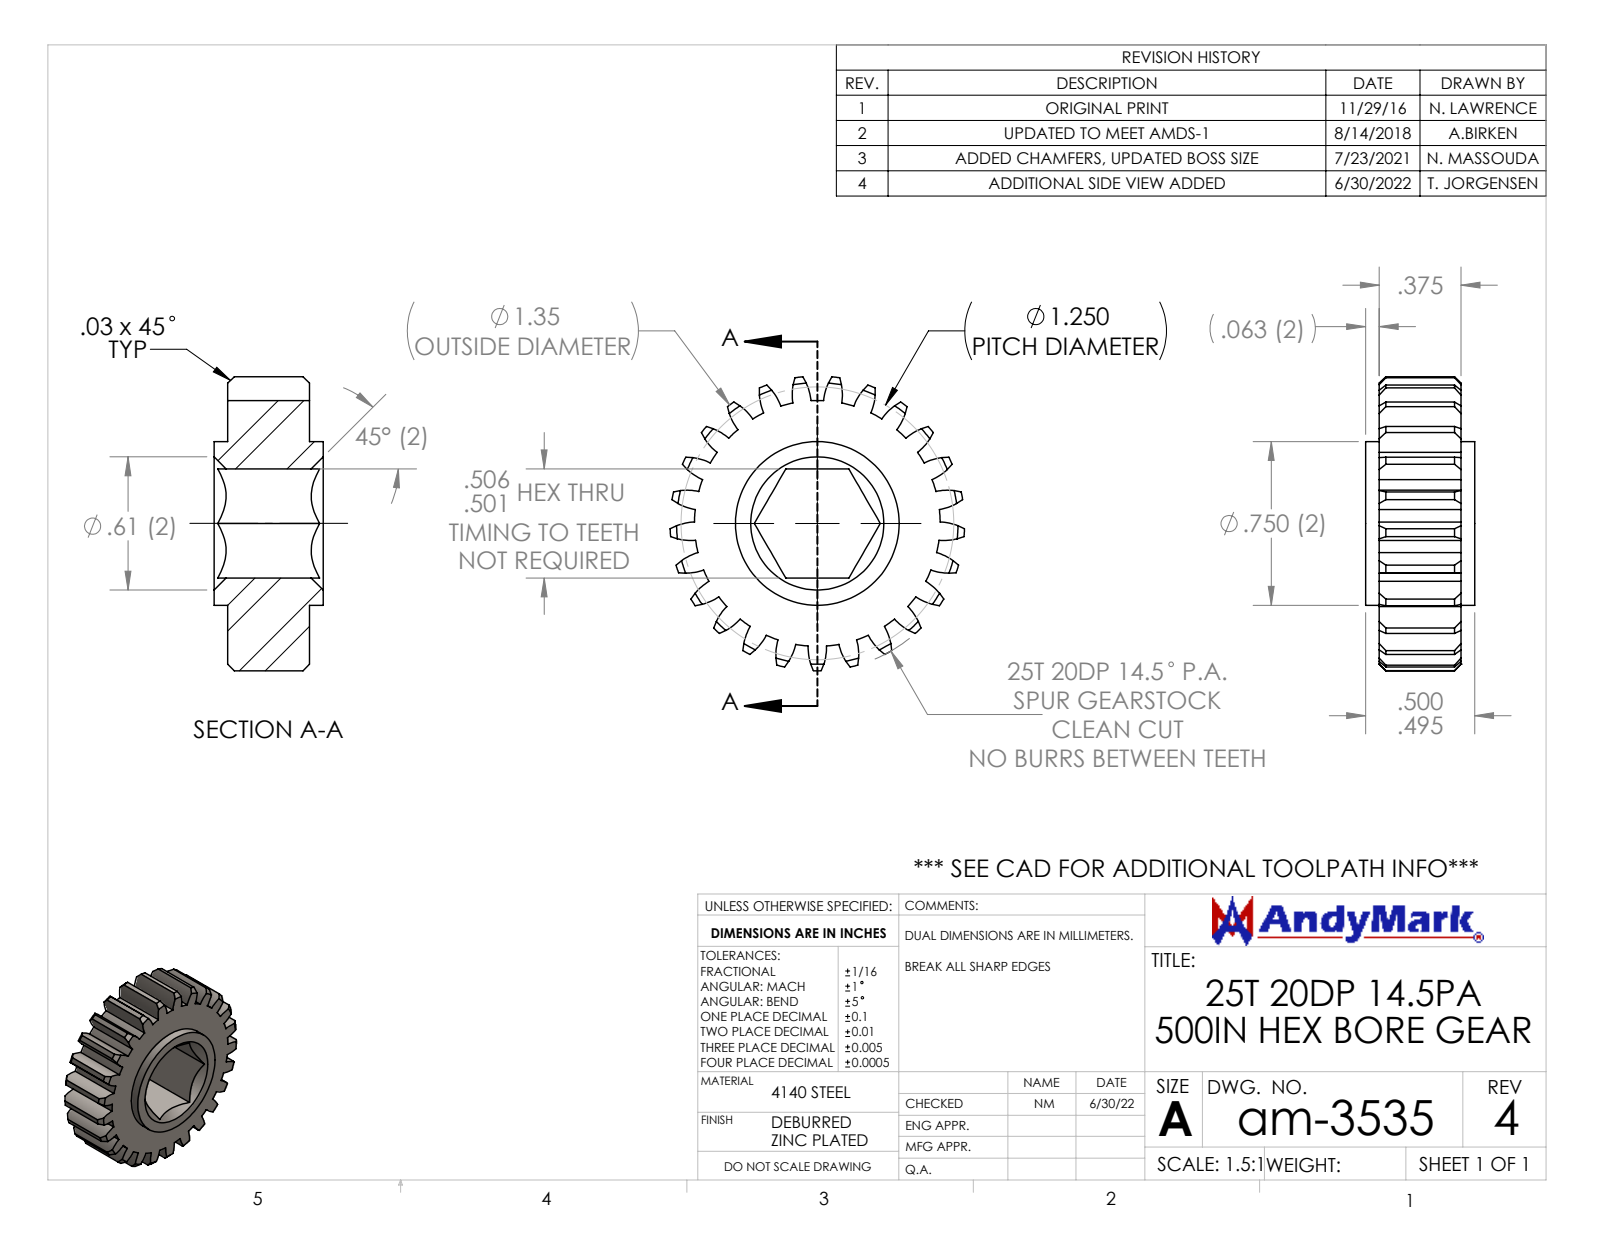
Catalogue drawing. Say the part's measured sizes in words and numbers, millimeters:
The part is named "am-3535 25T 20DP 500hex 375 FW Gear". Its 3-D file was written by "SolidWorks 2021 (CONFIG_CONTROL_DESIGN)". It is 1 solid with 172 faces: 10 planar, 108 cylindrical and 54 other. Overall it measures 34.3 by 34.2 by 12.7 millimeters. Its volume is 6 370 cubic millimeters and its surface area 3 887 square millimeters. Round bosses or shafts: 1 of diameter 19.1. Partial cylindrical surfaces (rounded edges, fillets, slot ends): 50 of radius 6.4, 1 of radius 14.3, 1 of radius 17.1. The main face-to-face distances are 9.5, 12.7, 11.1, 1.6, 1.6, 11.1.
